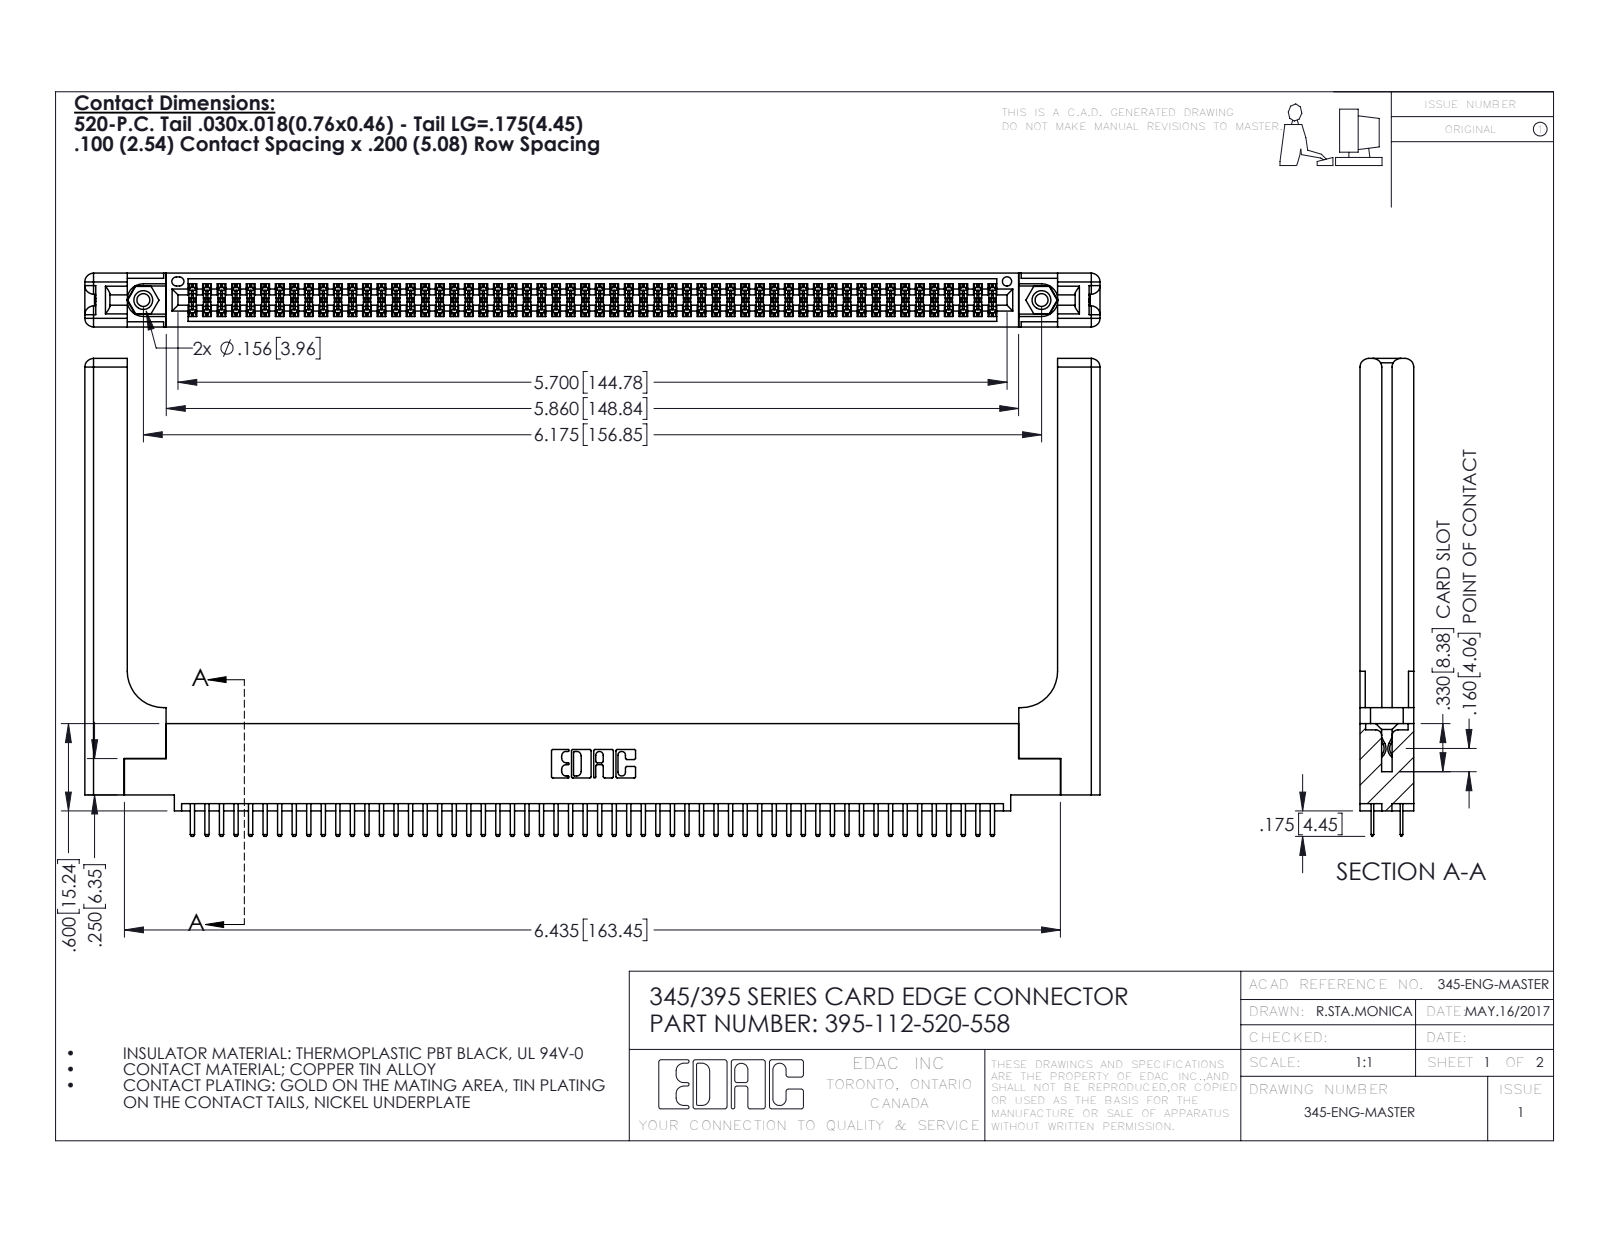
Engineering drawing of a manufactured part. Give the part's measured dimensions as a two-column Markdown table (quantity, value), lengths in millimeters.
| quantity | value |
| --- | --- |
| part name | 345-292-001_345-293-120; 345-250-001_345-250-001-102; 395-112-520-558; 345-220-058_345-220-058 (+1 more) |
| STEP written by | SolidWorks 2016 (CONFIG_CONTROL_DESIGN) |
| units | millimeters |
| bodies | 117 solids, 6434 faces (4152 planar, 2222 cylindrical, 60 other) |
| overall size | 177.3 × 83.4 × 9.4 |
| volume | 25 690 mm³ |
| surface area | 30 780 mm² |
| round holes (diameter × count) | 2.3 × 2, 3.2 × 2, 4 × 2, 1.6 × 1 |
| round bosses / shafts (diameter × count) | 3.9 × 2 |
| partial cylindrical surfaces (radius × count) | 0.2 × 168, 0.3 × 116, 0.3 × 22, 1.5 × 16, 0.2 × 6, 0.8 × 6, 0.7 × 3, 0.4 × 2 |
| main face-to-face distances | 1.8, 7.6, 9.4, 5.1, 2.5, 6.9, 0.6, 5.7, 0.6, 3.8 |
| hole center spacings | 6.9, 150.9, 156.8 |
